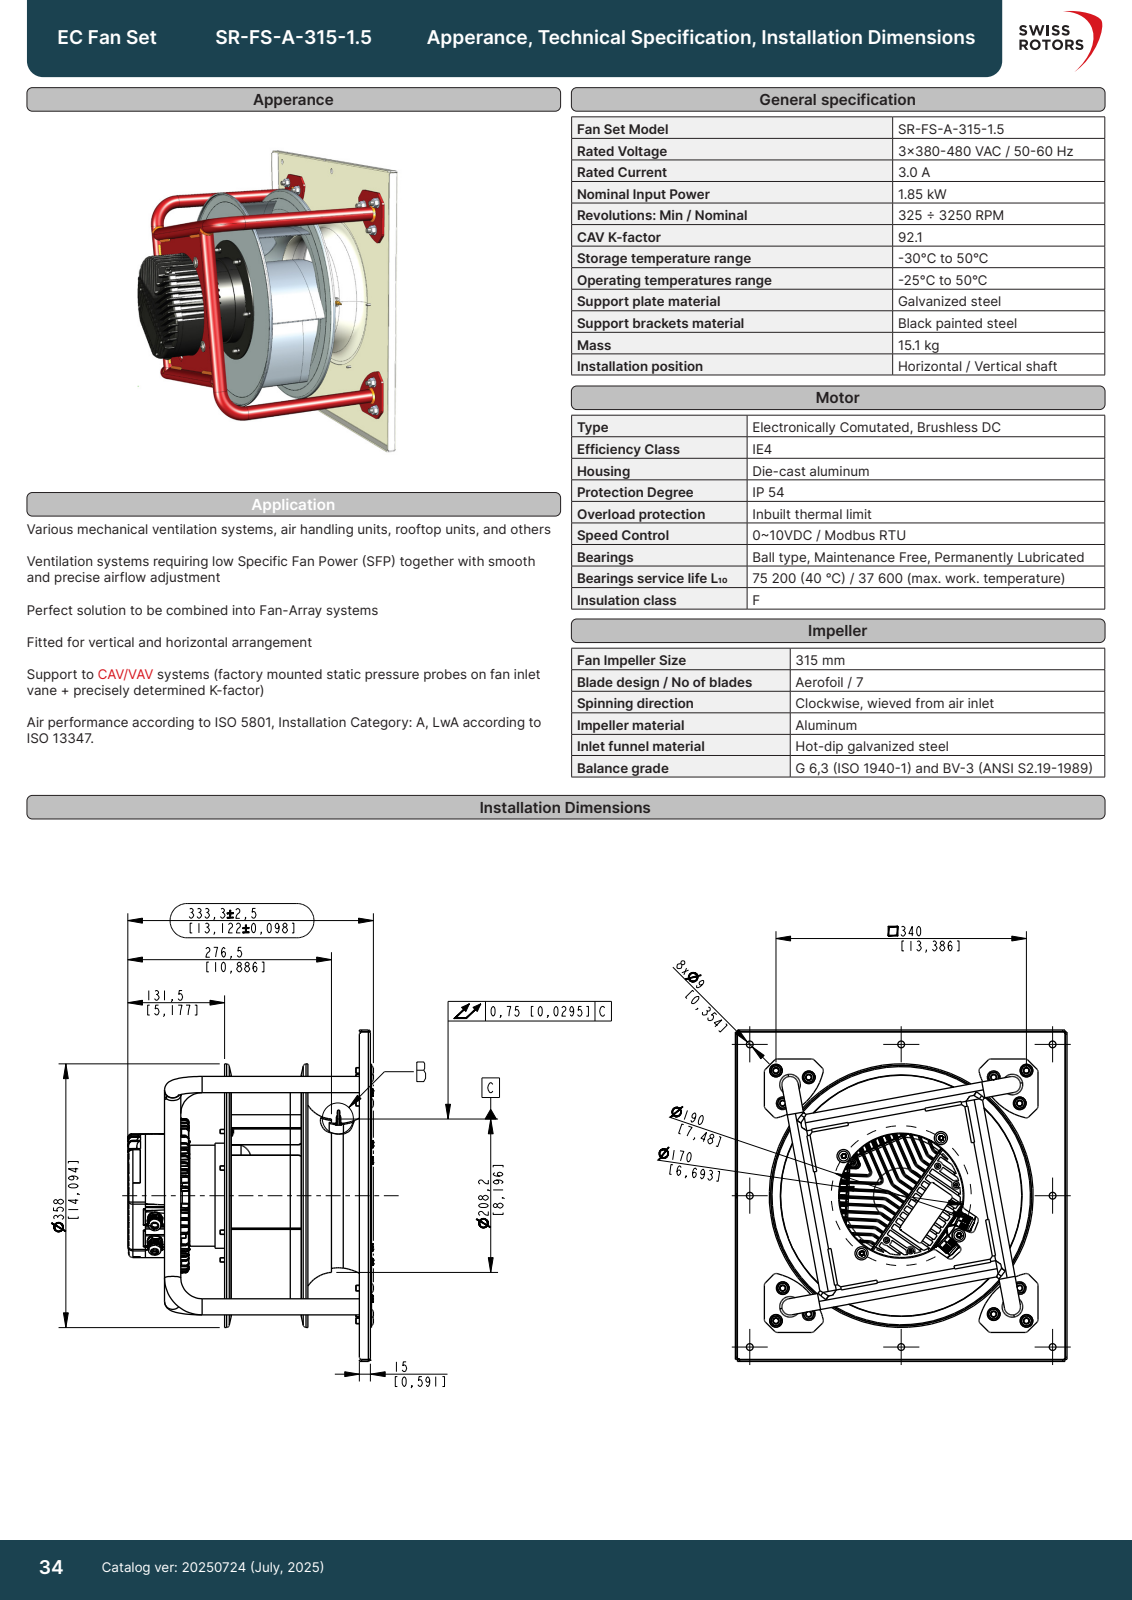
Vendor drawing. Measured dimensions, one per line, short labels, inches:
name: 1187559; 1187560; FILLET_WELD_ID_1315; 1176184 (+8 more)
written by: CREO PARAMETRIC BY PTC INC, 2022484 (CONFIG_CONTROL_DESIGN)
unit: in
bodies: 50 solids, 6195 faces (1823 planar, 2304 cylindrical, 2068 other)
size: 17.717 × 17.717 × 12.807
volume: 626.7 in³; area: 2 399 in²
holes: 12× ⌀0.354, 7× ⌀0.177, 6× ⌀0.122, 6× ⌀0.197, 6× ⌀0.252, 6× ⌀0.346, 6× ⌀0.551, 5× ⌀0.193, 4× ⌀0.256, 4× ⌀0.268, 4× ⌀0.315, 4× ⌀0.331
bosses: 8× ⌀0.697, 6× ⌀0.512, 6× ⌀0.433, 6× ⌀0.354, 6× ⌀0.236, 6× ⌀0.157, 4× ⌀0.709, 4× ⌀0.315
rounds: 484× R0.039, 346× R0.024, 168× R0.059, 144× R0.335, 124× R0.02, 108× R0.167, 108× R0.245, 48× R0.027
face distances: 0.079, 7.496, 7.417, 0.098, 10.488, 0.118, 7.516, 10.567, 3.071, 10.685
hole spacings: 5.512, 3.445, 6.544, 11.581, 4.304, 12.205, 3.186, 3.445
